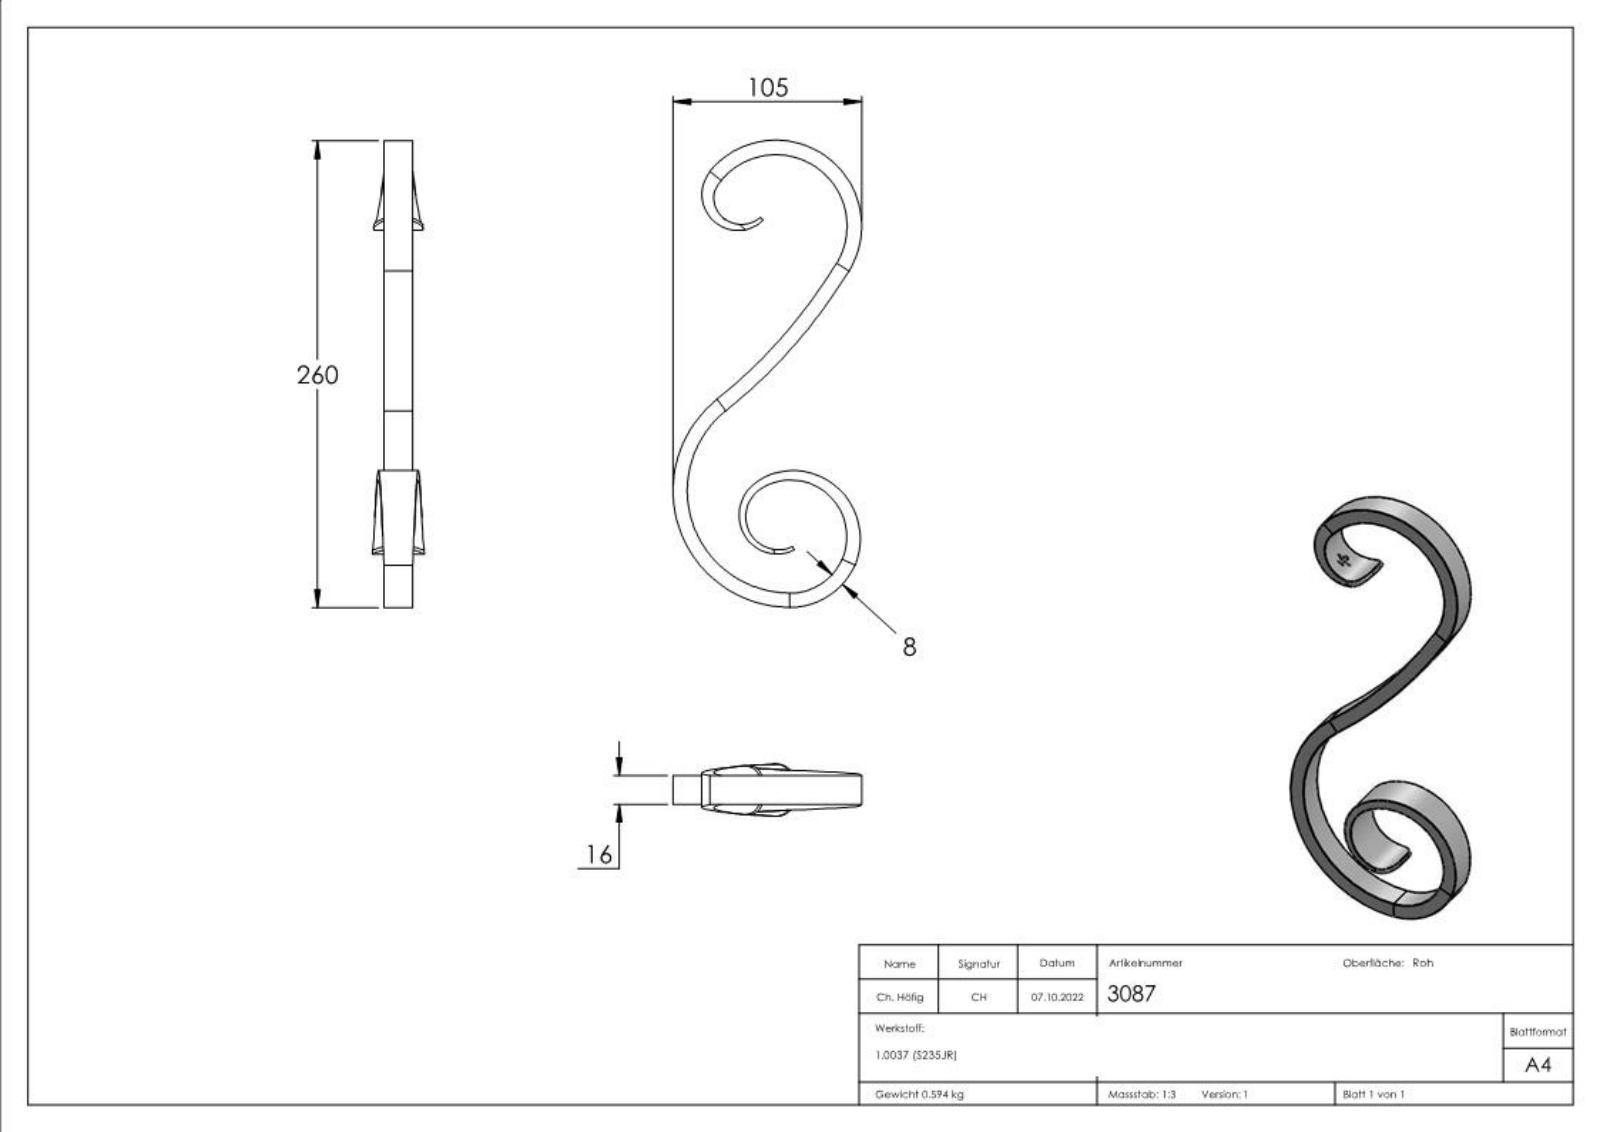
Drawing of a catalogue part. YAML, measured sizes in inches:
part_name: "3087"
step_written_by: "SolidWorks 2018 (CONFIG_CONTROL_DESIGN)"
units: inches
bodies: {solids: 1, faces: 242, planar: 95, cylindrical: 8, other: 139}
overall_size: [10.236, 4.134, 1.141]
volume: 4.645
surface_area: 49
partial_cylinders:
  - {radius: 1.26, count: 1}
  - {radius: 1.563, count: 1}
  - {radius: 1.575, count: 1}
  - {radius: 1.878, count: 1}
  - {radius: 2.244, count: 1}
  - {radius: 2.559, count: 1}
  - {radius: 11.4, count: 1}
  - {radius: 11.715, count: 1}
face_to_face_distances: [0.63, 0.124, 0.079, 0.117, 0.05, 0.315, 0.013, 0.065, 0.015, 0.072]
